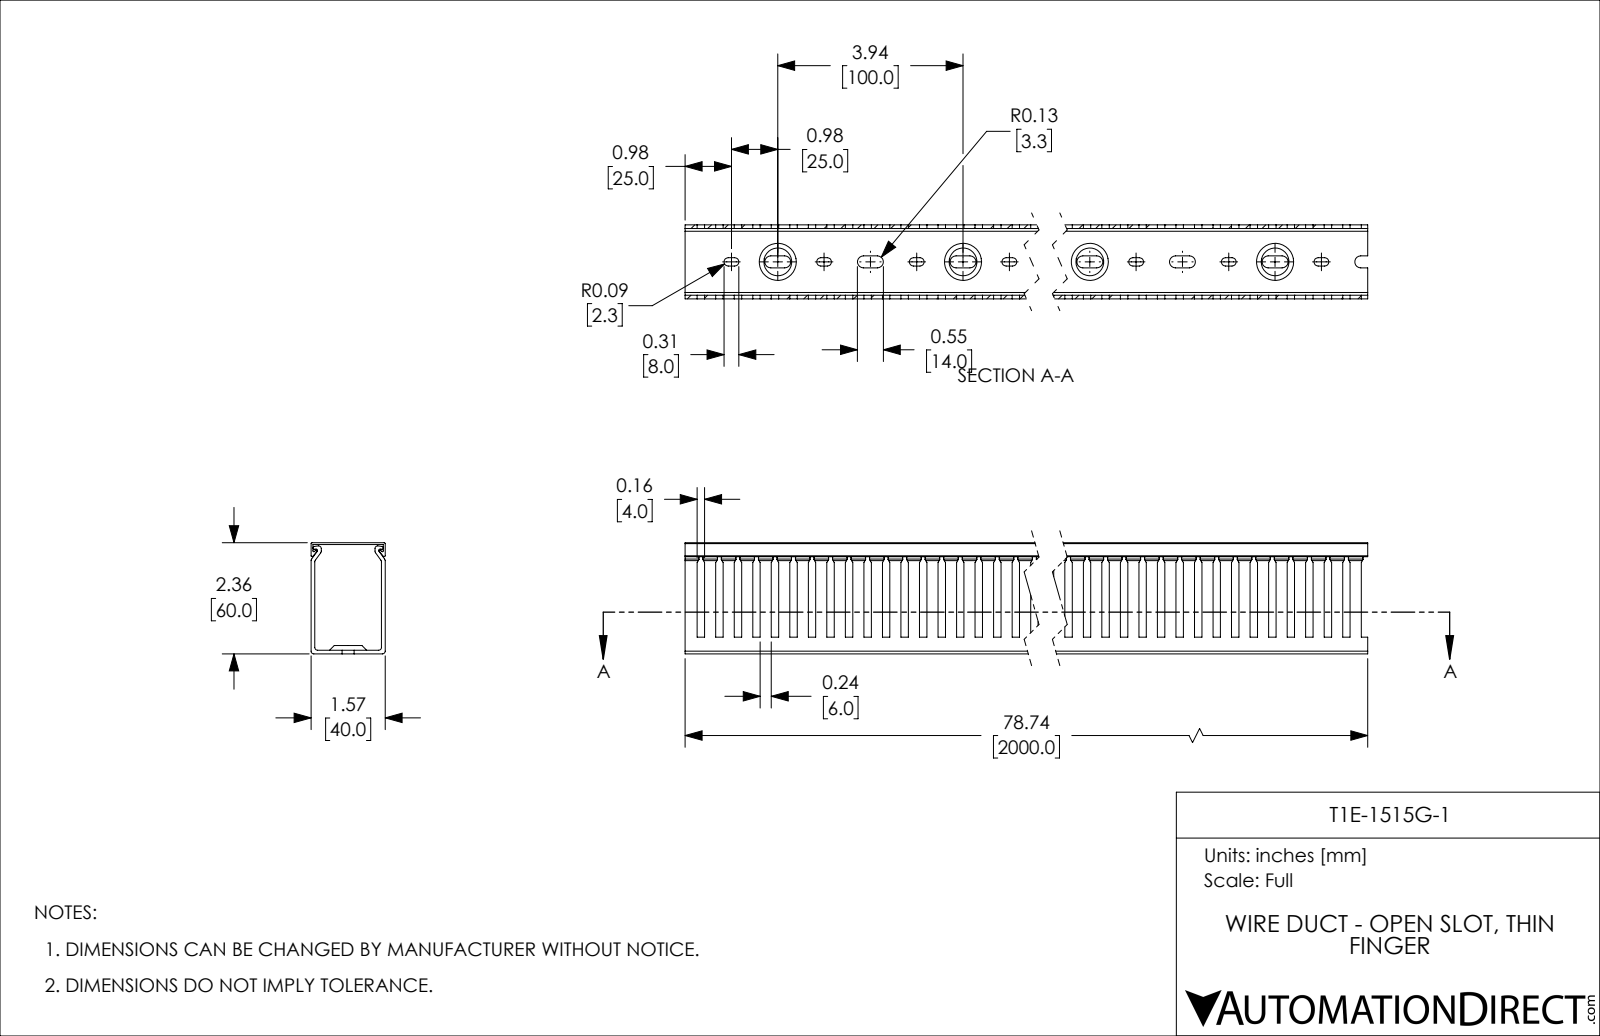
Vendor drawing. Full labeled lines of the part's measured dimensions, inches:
Part name (STEP PRODUCT): T1E-1522G-1
STEP written by: SolidWorks 2021 (CONFIG_CONTROL_DESIGN)
Units: inches
Bodies: 2 solids, 1005 faces (534 planar, 431 cylindrical, 40 other)
Overall size (bounding box): 78.74 × 2.362 × 1.575
Volume: 45.26 in³ · Surface area: 1 330 in²
Partial cylindrical surfaces — rounded edges, fillets, slot ends (radius × count): R0.089 ×80, R0.128 ×80, R0.059 ×12, R0.02 ×8, R0.03 ×6
Main face-to-face distances: 0.079, 1.496, 1.575, 0.039, 1.417, 2.362, 2.323, 2.244, 2.283, 1.535
